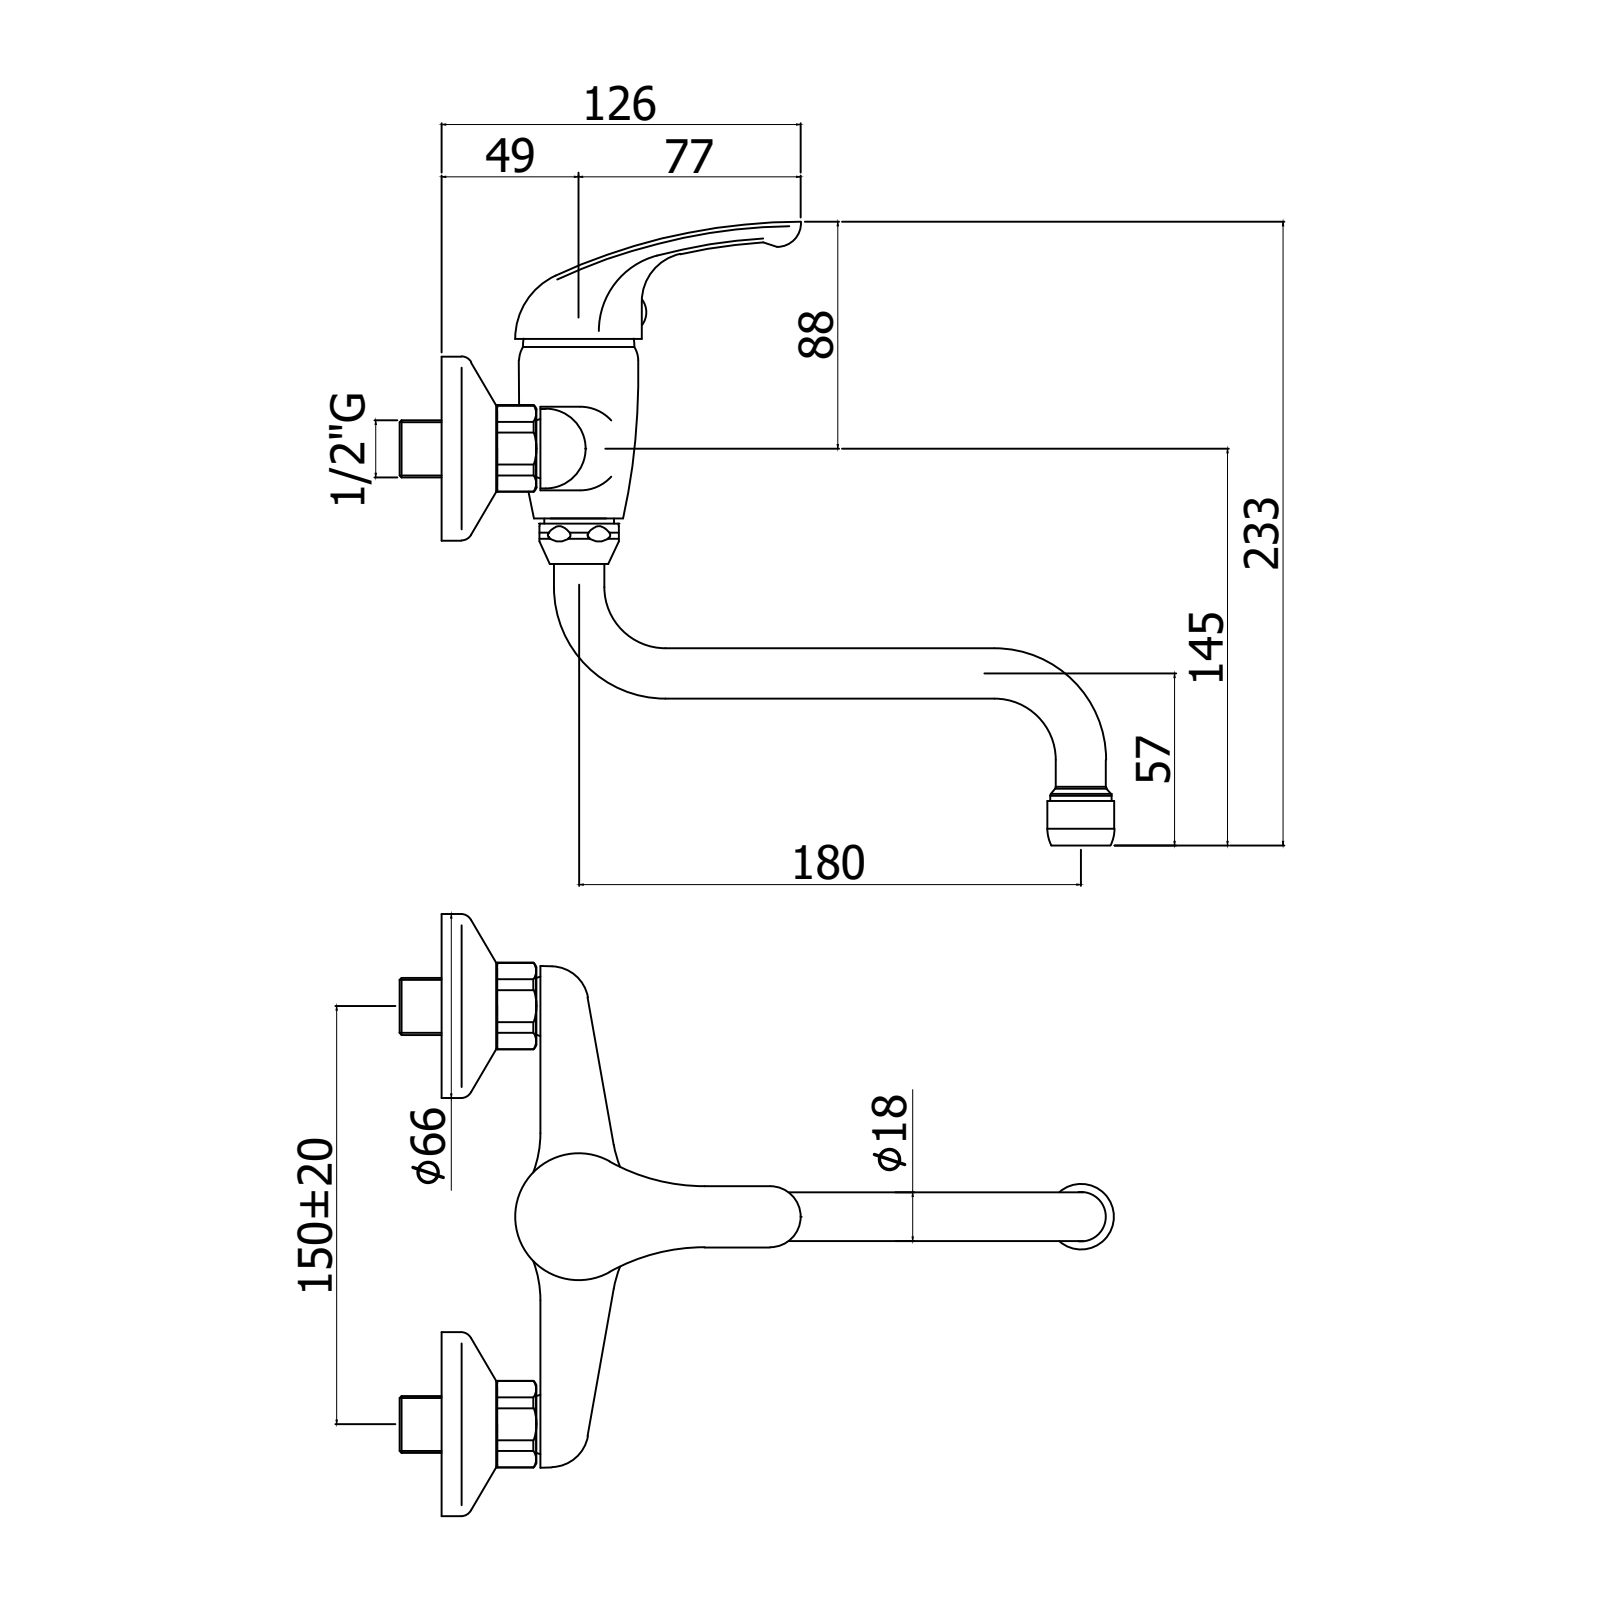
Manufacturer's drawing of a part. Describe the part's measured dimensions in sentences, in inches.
The part is named "APM3164CR". Its 3-D file was written by "CREO PARAMETRIC BY PTC INC, 2020044 (CONFIG_CONTROL_DESIGN)". It is 4 solids with 3012 faces: 2120 planar, 408 cylindrical and 484 other. Overall it measures 9.48 by 9.181 by 8.504 inches. Its volume is 9.044 cubic inches and its surface area 217.4 square inches. Round holes: 3 of diameter 0.354, 3 of diameter 0.472, 3 of diameter 0.654, 2 of diameter 0.157, 2 of diameter 0.276, 2 of diameter 0.315, 2 of diameter 0.413, 2 of diameter 0.709, 2 of diameter 0.846, 2 of diameter 0.949, 2 of diameter 0.984, 2 of diameter 1.051. Round bosses or shafts: 3 of diameter 0.709, 2 of diameter 2.598, 2 of diameter 1.008, 2 of diameter 0.945, 1 of diameter 1.378, 1 of diameter 1.37, 1 of diameter 1.331, 1 of diameter 1.268. Partial cylindrical surfaces (rounded edges, fillets, slot ends): 41 of radius 0.02, 12 of radius 0.039, 11 of radius 0.006, 9 of radius 0.012, 4 of radius 0.276, 2 of radius 0.138, 2 of radius 0.177, 2 of radius 0.313. The main face-to-face distances are 0.138, 0.02, 0.118, 0.236, 0.335, 0.374, 0.472, 0.354, 0.177, 0.098. The hole center spacings are 0.028, 0.335, 0.339, 0.513, 0.52, 0.532, 3.52, 3.733.
